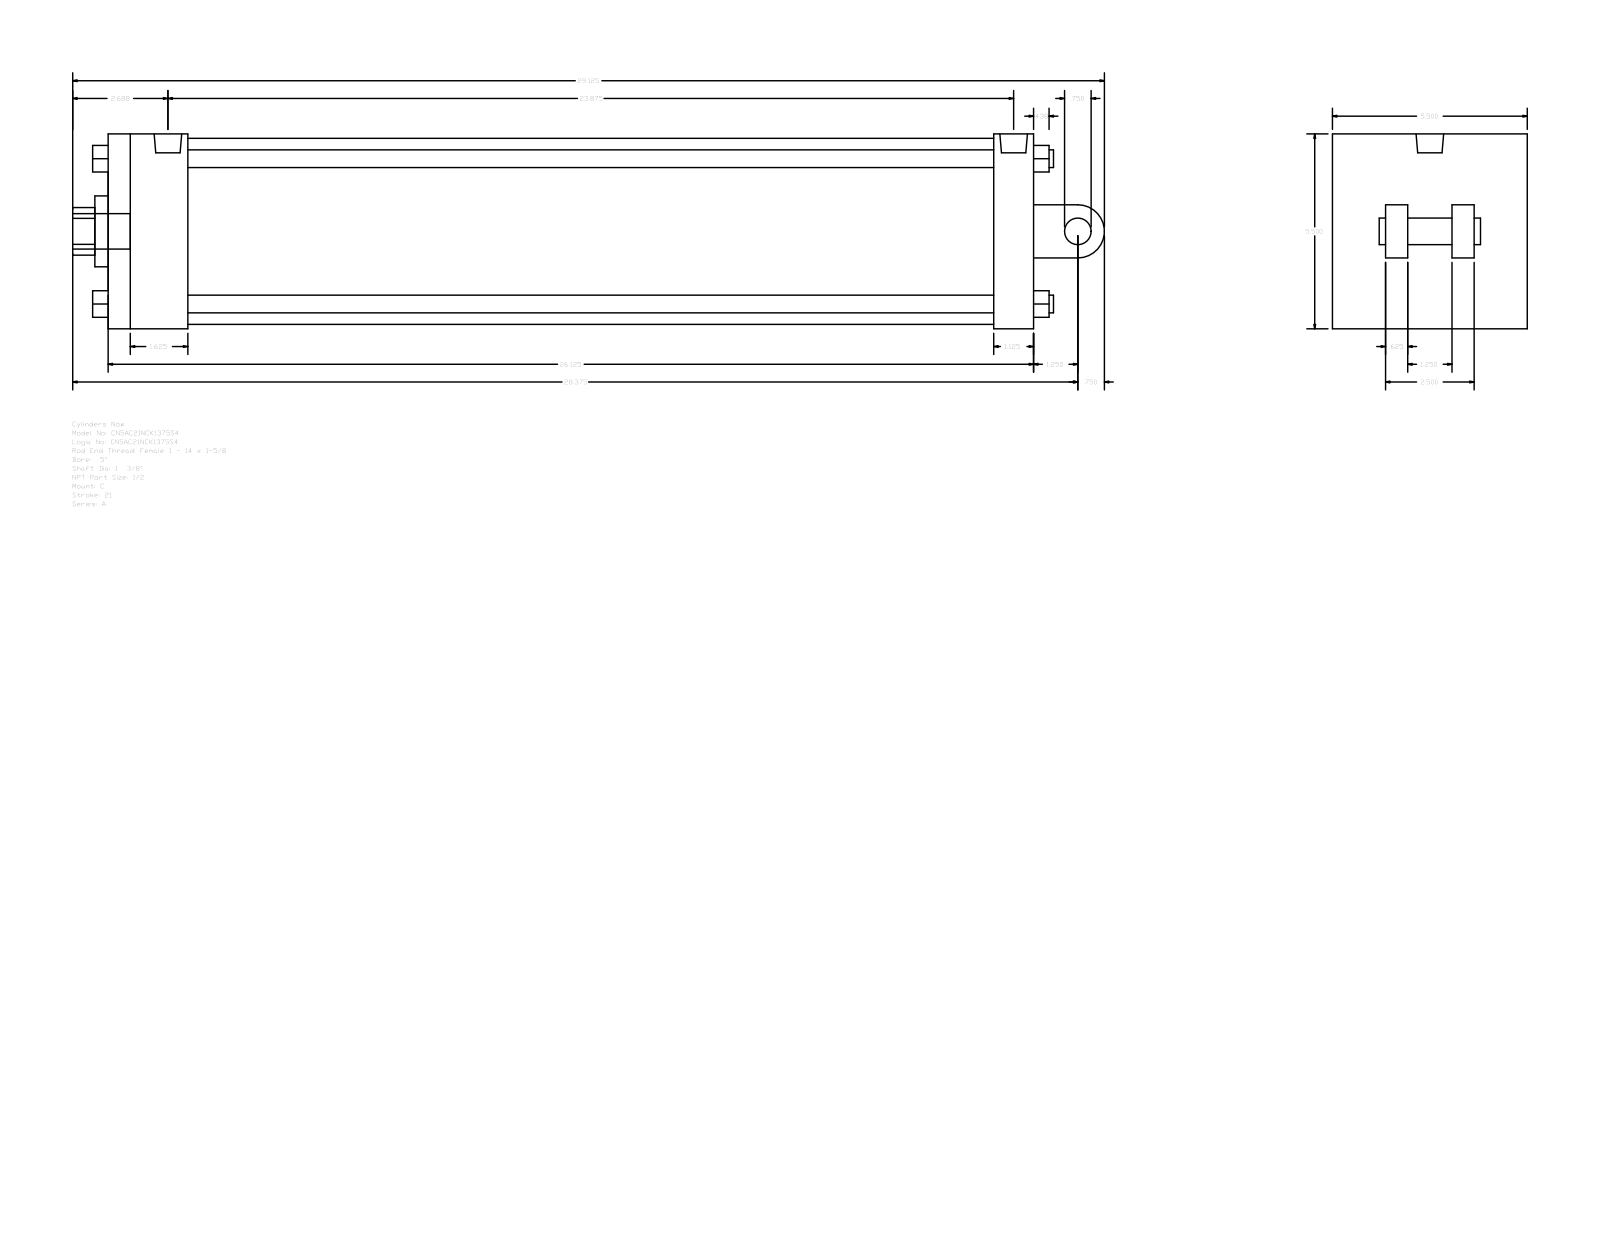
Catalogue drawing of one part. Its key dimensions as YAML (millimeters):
part_name: "A_C__0500_1.375"
step_written_by: "GSSL Pune (CONFIG_CONTROL_DESIGN)"
units: millimeters
bodies: {solids: 0, faces: 135, planar: 102, cylindrical: 33, other: 0}
overall_size: [739.77, 139.7, 139.7]
round_holes:
  - {diameter: 8.73, count: 2}
  - {diameter: 19.77, count: 1}
  - {diameter: 34.92, count: 1}
  - {diameter: 50.8, count: 1}
  - {diameter: 133.35, count: 1}
round_bosses_or_shafts:
  - {diameter: 12.7, count: 4}
  - {diameter: 8.73, count: 2}
  - {diameter: 25.4, count: 1}
  - {diameter: 19.77, count: 1}
  - {diameter: 19.05, count: 1}
partial_cylinders:
  - {radius: 17.06, count: 1}
  - {radius: 19.05, count: 1}
face_to_face_distances: [139.7, 663.58, 28.58, 57.15, 635, 577.85, 606.43, 38.1, 15.87, 53.97]
hole_center_spacings: [2.39]
